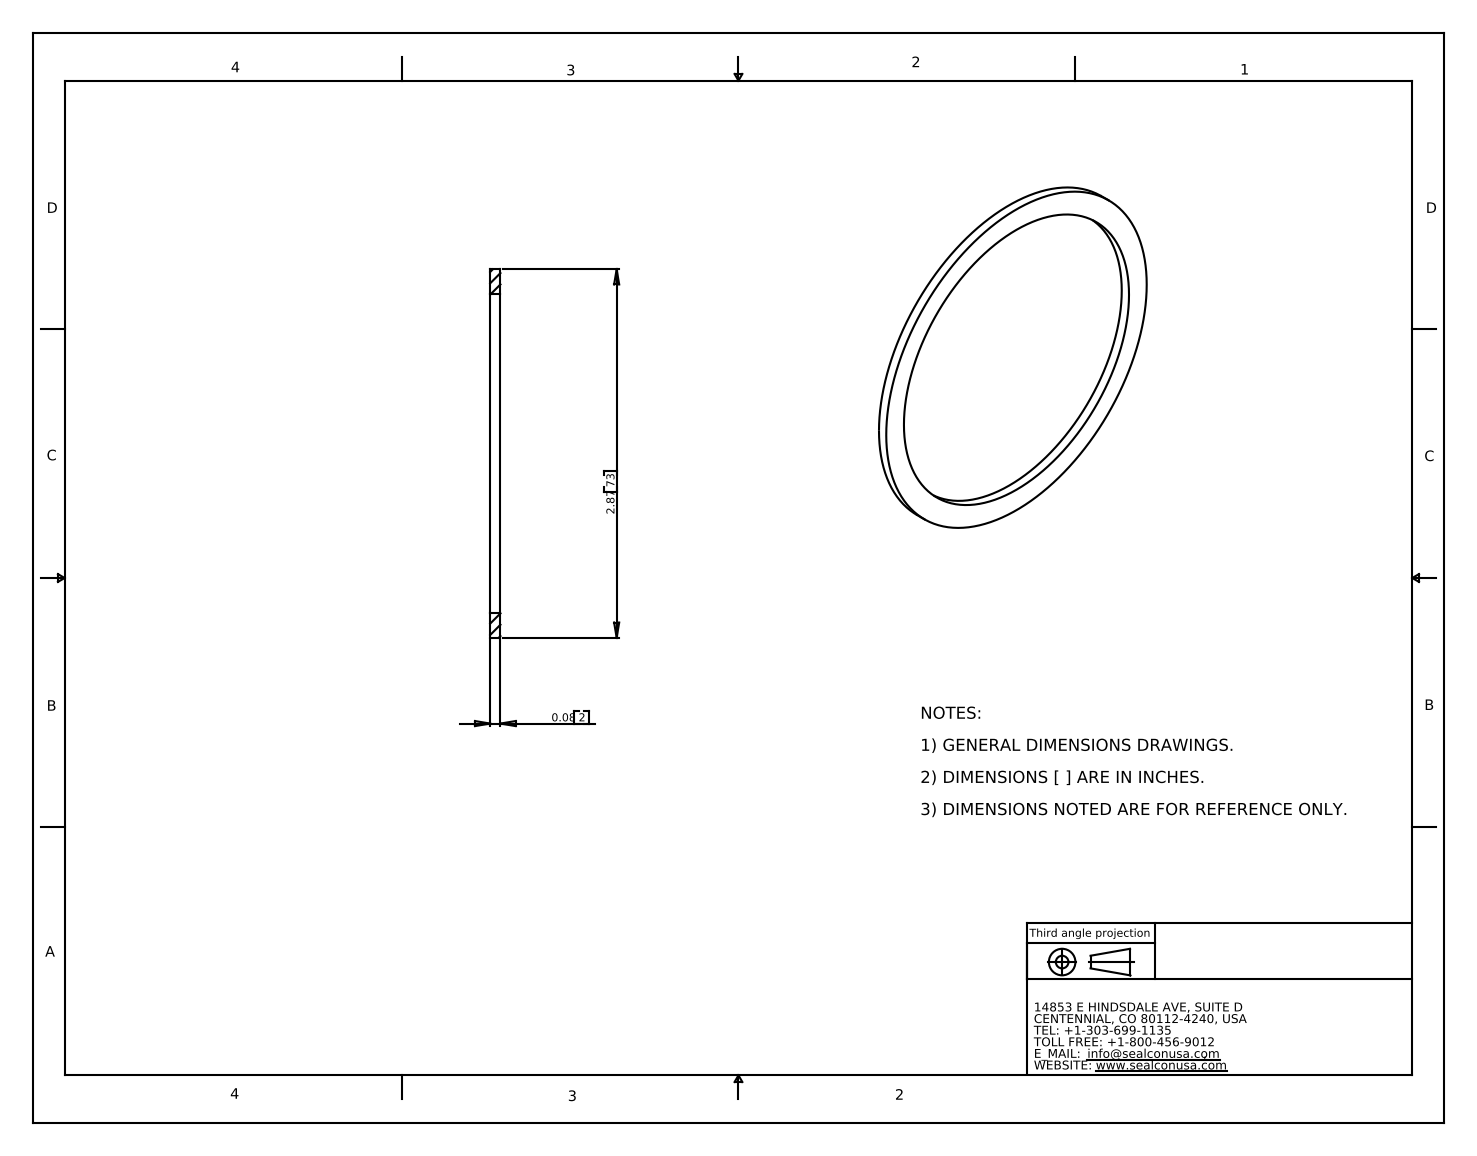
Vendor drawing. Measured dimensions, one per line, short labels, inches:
name: SM-63-VT
written by: SolidWorks 2007 (CONFIG_CONTROL_DESIGN)
unit: in
bodies: 1 solid, 6 faces (2 planar, 4 cylindrical, 0 other)
size: 2.87 × 2.87 × 0.08
volume: 0.131 in³; area: 4.622 in²
holes: 1× ⌀2.48
bosses: 1× ⌀2.87
face distances: 0.08
